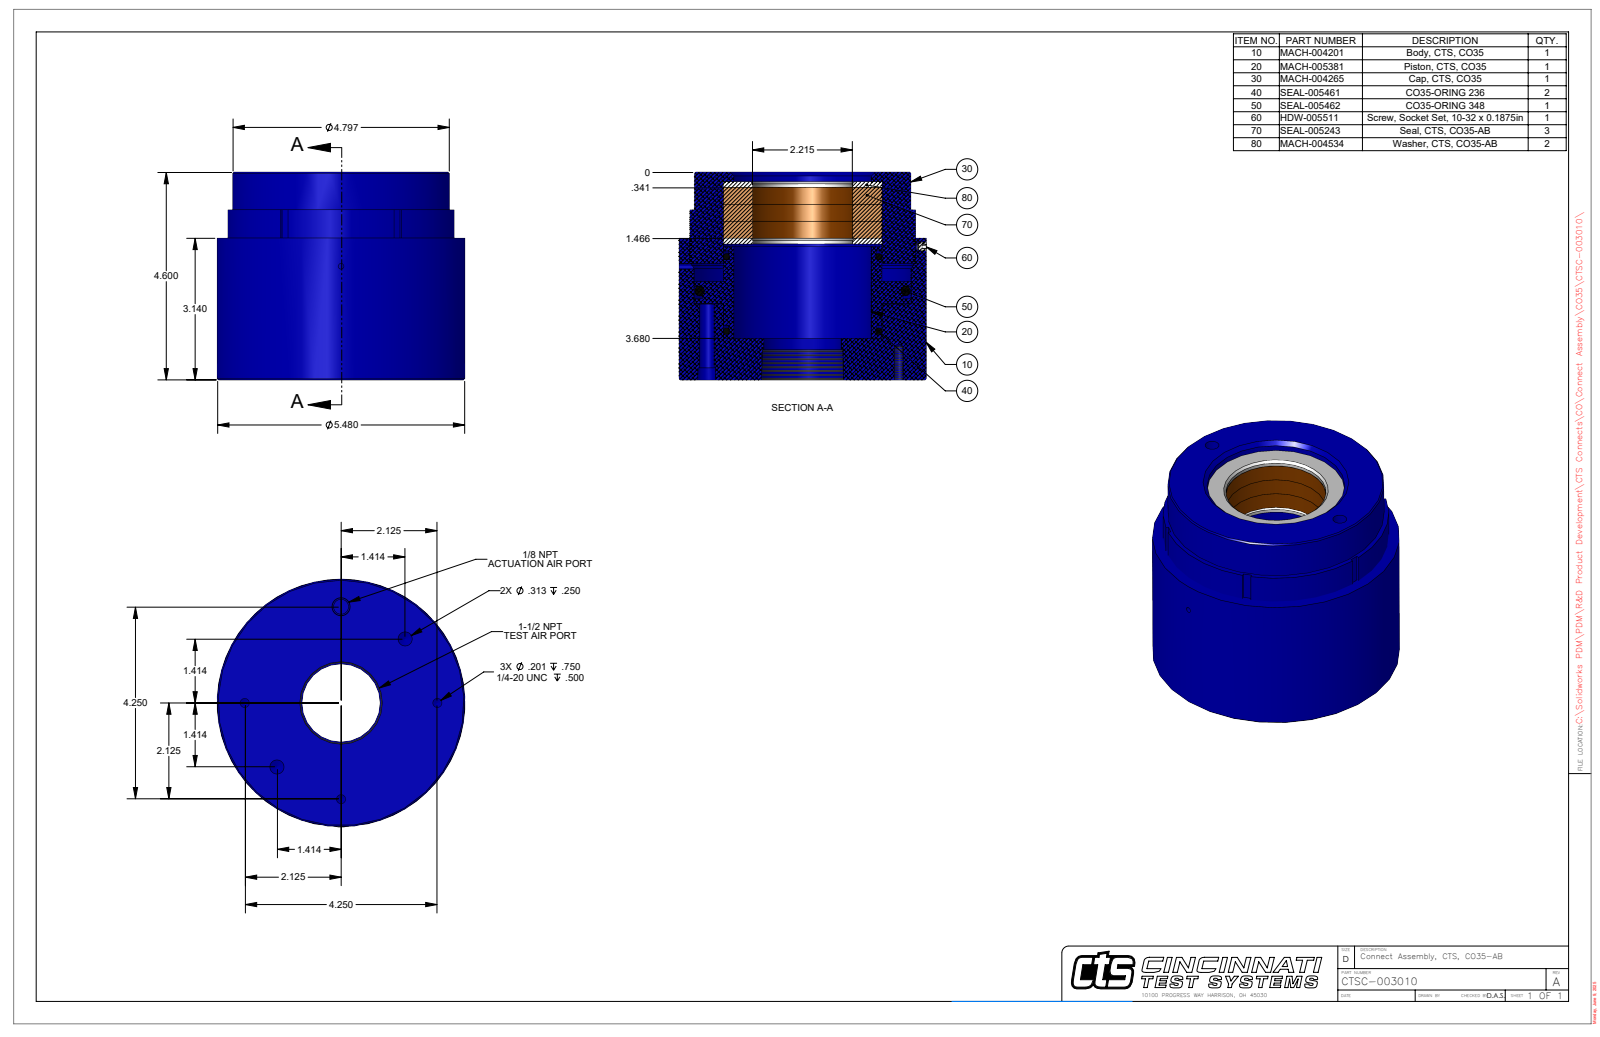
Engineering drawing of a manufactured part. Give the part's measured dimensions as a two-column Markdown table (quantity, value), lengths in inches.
| quantity | value |
| --- | --- |
| part name | CTSC-003010 |
| STEP written by | SolidWorks 2023 (AUTOMOTIVE_DESIGN) |
| units | inches |
| bodies | 2 solids, 132 faces (50 planar, 58 cylindrical, 24 other) |
| overall size | 5.486 × 5.48 × 4.6 |
| volume | 76.63 in³ |
| surface area | 185.7 in² |
| round holes (diameter × count) | 0.313 × 4, 0.201 × 3, 0.125 × 1, 0.332 × 1, 1.719 × 1, 2.215 × 1, 2.217 × 1, 3.05 × 1, 3.108 × 1, 3.517 × 1 |
| round bosses / shafts (diameter × count) | 5.48 × 1, 5 × 1, 4.797 × 1, 3.513 × 1, 3.509 × 1 |
| partial cylindrical surfaces (radius × count) | 2.46 × 1, 2.722 × 1 |
| main face-to-face distances | 4.259, 4.6, 0.341, 0.125, 4.384, 0.216, 0.92, 3.339, 3.464, 3.68 |
| hole center spacings | 1.583, 2, 2.125, 2.918, 3.005, 3.811, 0.125, 1.531 |
